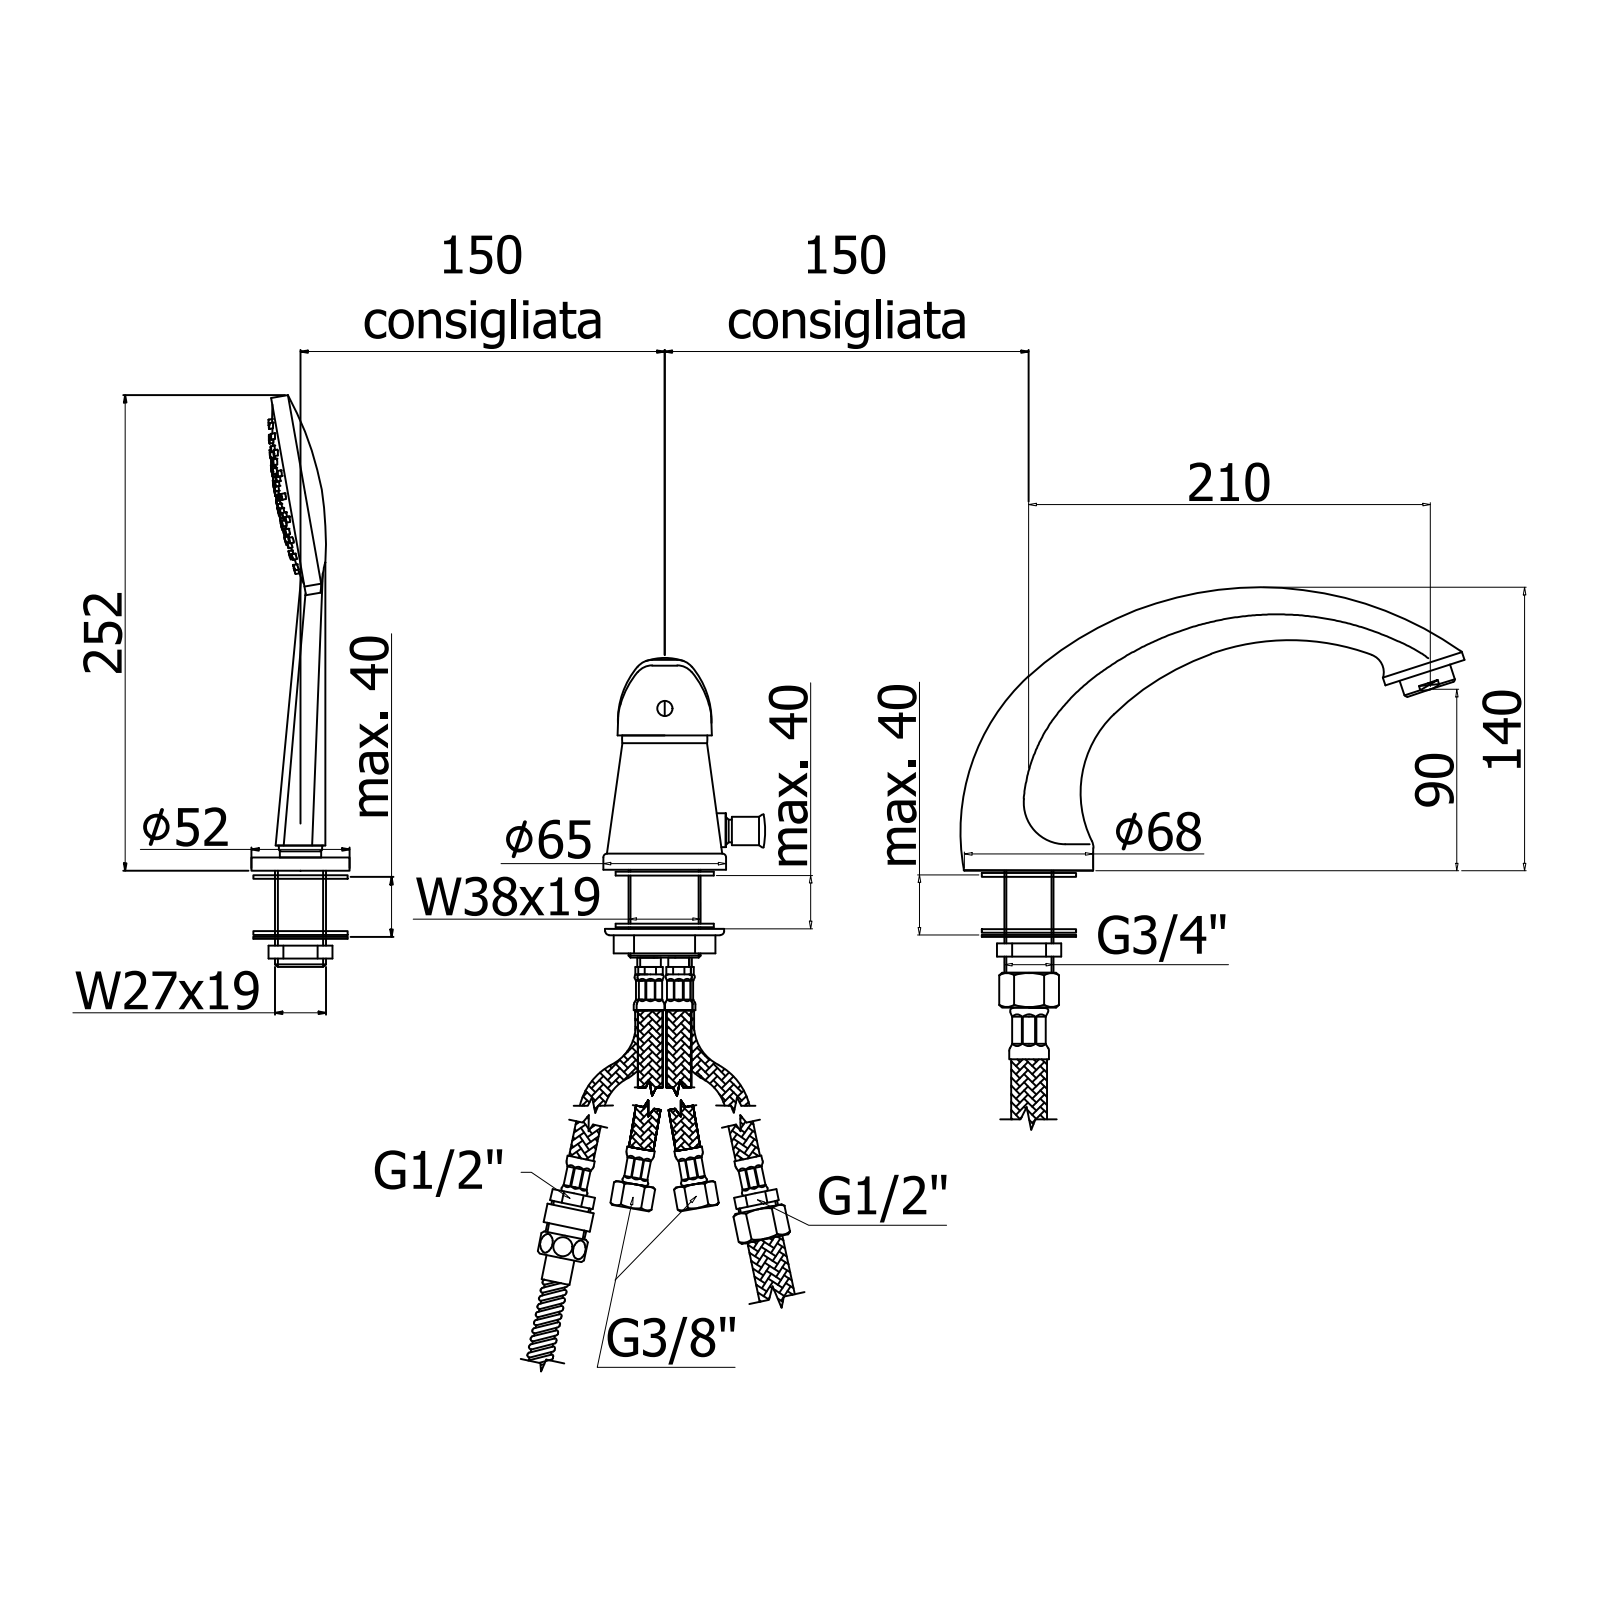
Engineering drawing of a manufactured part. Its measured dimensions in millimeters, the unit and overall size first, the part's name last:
Units: millimetres
Overall size (bounding box): 386.5 × 267.6 × 252.7
Round holes (diameter × count): ⌀7 ×7, ⌀5.5 ×2, ⌀40.5 ×2, ⌀3.5 ×1, ⌀4.5 ×1, ⌀6 ×1, ⌀7.8 ×1, ⌀9.2 ×1, ⌀9.5 ×1, ⌀13 ×1, ⌀13.5 ×1, ⌀15.2 ×1
Round bosses / shafts (diameter × count): ⌀3 ×90, ⌀105 ×1, ⌀65 ×1, ⌀52 ×1, ⌀44.5 ×1, ⌀42 ×1, ⌀28 ×1, ⌀21 ×1
Partial cylindrical surfaces — rounded edges, fillets, slot ends (radius × count): R1.5 ×2, R15 ×2, R24 ×2, R24.5 ×2, R18 ×1, R39.04 ×1, R340.59 ×1, R341.58 ×1
Main face-to-face distances: 7, 12, 5, 10, 14, 2, 3.5, 1.5, 5.5, 8.5
Hole centre spacings: 15.61, 9.23, 9.24, 14, 16.76, 24.84, 24
Volume: 934 218 mm³ · Surface area: 139 366 mm²
Bodies: 5 solids, 568 faces (65 planar, 269 cylindrical, 234 other)
Part name (STEP PRODUCT): DU040CR
STEP written by: CREO PARAMETRIC BY PTC INC, 2020044 (CONFIG_CONTROL_DESIGN)
